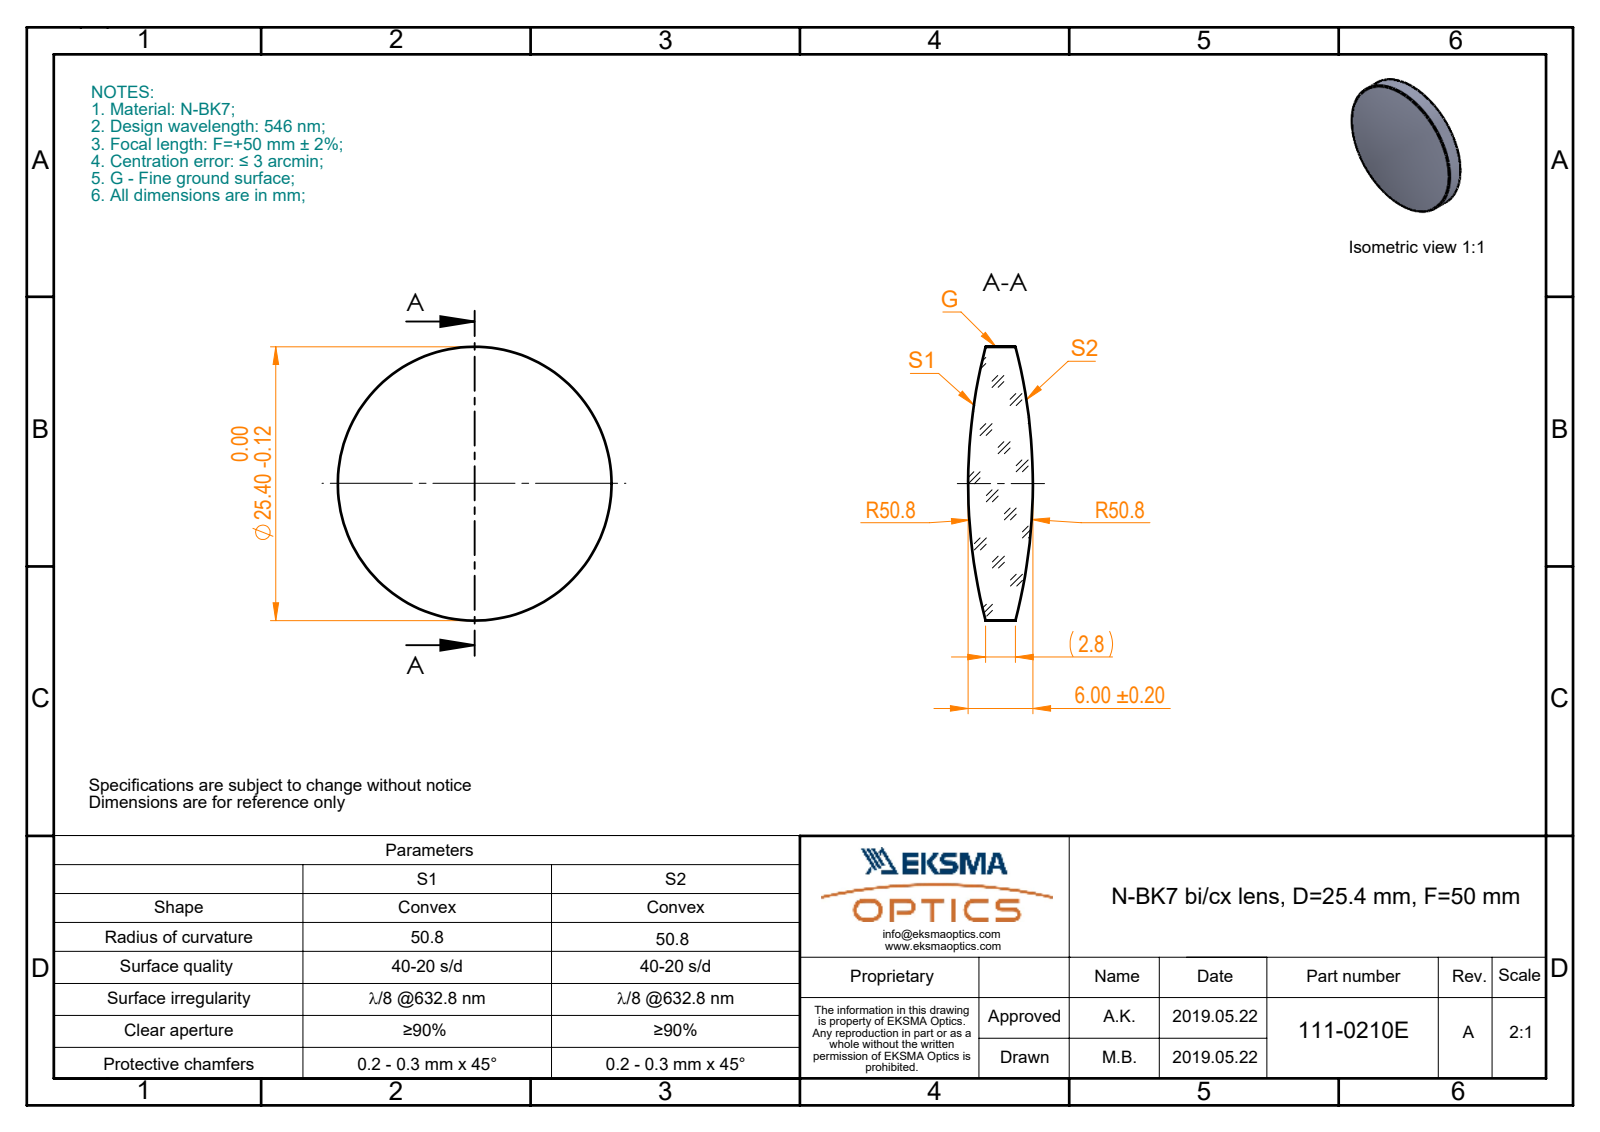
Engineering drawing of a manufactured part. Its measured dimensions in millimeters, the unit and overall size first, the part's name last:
Units: millimetres
Overall size (bounding box): 25.4 × 25.4 × 6
Round bosses / shafts (diameter × count): ⌀25.4 ×1
Volume: 2 228 mm³ · Surface area: 1 251 mm²
Bodies: 1 solid, 6 faces (0 planar, 2 cylindrical, 4 other)
Part name (STEP PRODUCT): 111-0210E BK7 bi-cx 25.4 F50
STEP written by: SolidWorks 2017 (CONFIG_CONTROL_DESIGN)
